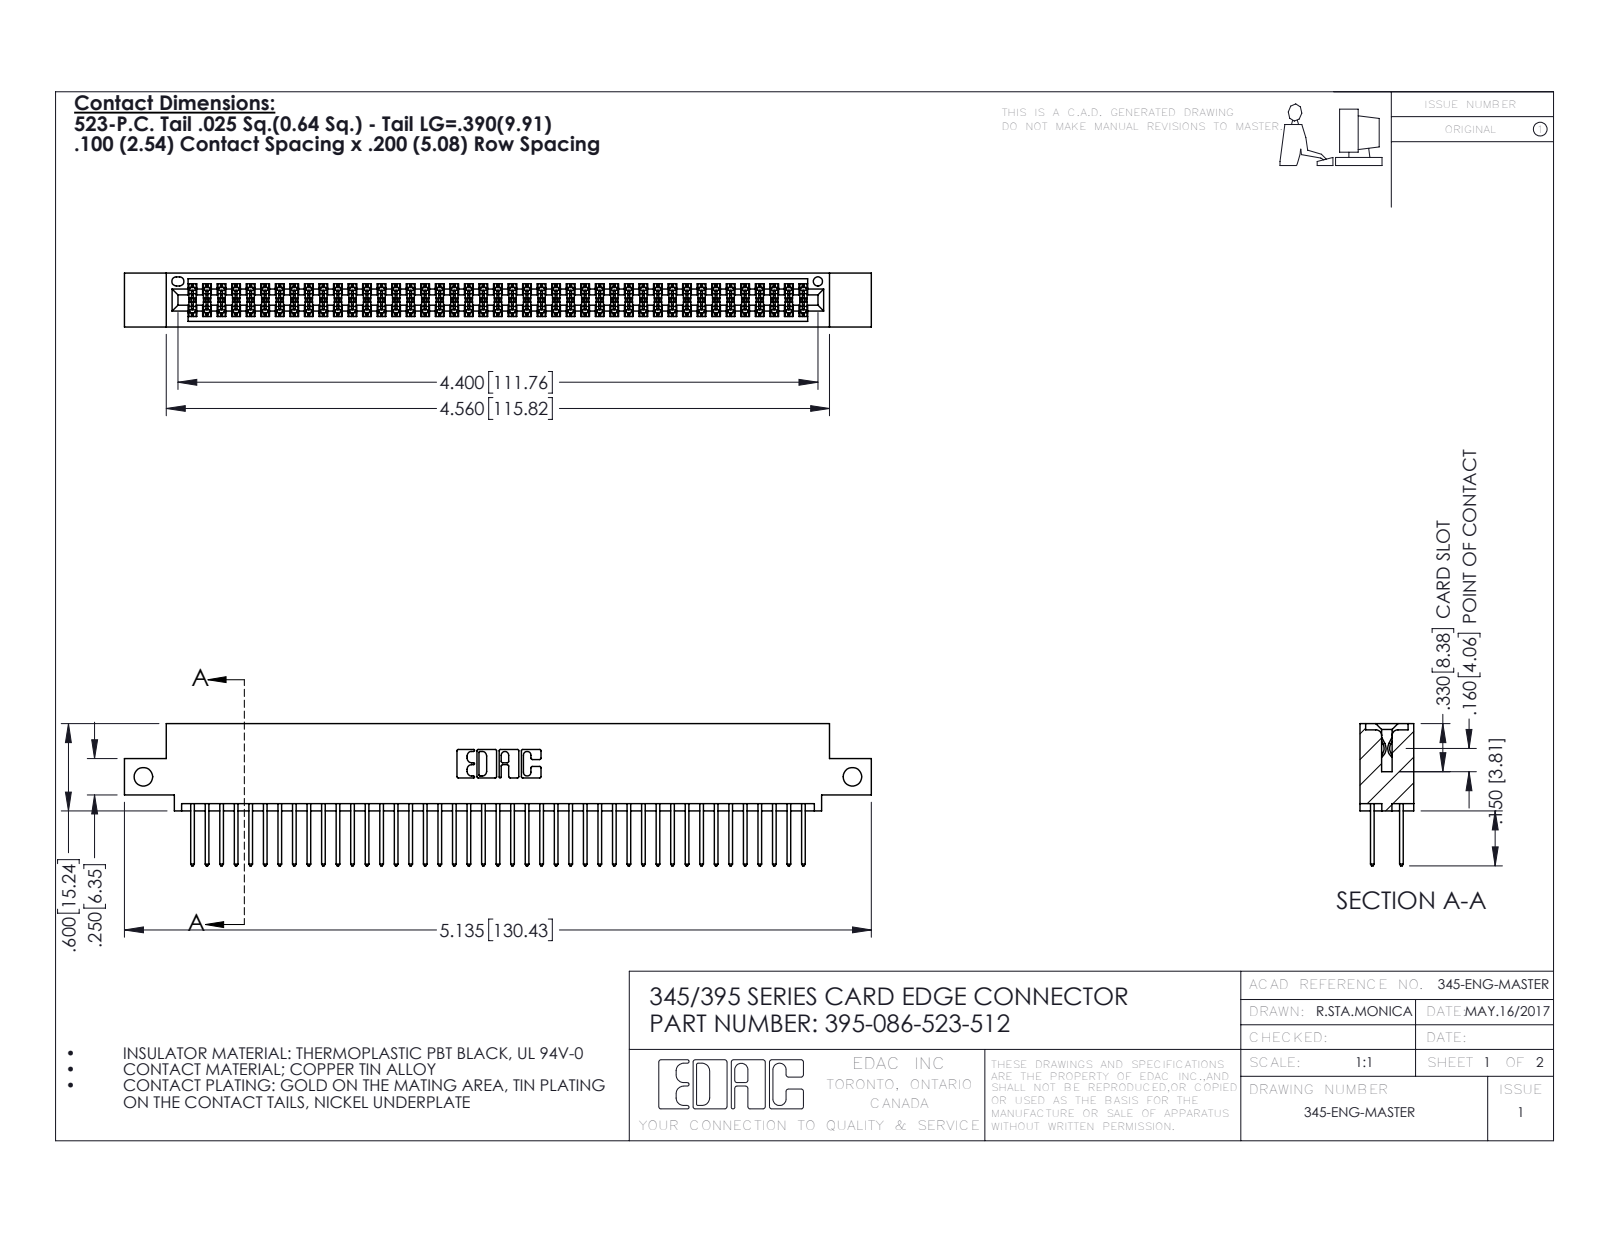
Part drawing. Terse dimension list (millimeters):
name: 395-086-523-512; 345-292-001_345-293-123; 345 Part_0.110 Offset - Side Mount
written by: SolidWorks 2016 (CONFIG_CONTROL_DESIGN)
unit: mm
bodies: 87 solids, 4430 faces (2922 planar, 1508 cylindrical, 0 other)
size: 130.4 × 24.8 × 9.4
volume: 12 700 mm³; area: 19 540 mm²
holes: 2× ⌀3.3, 1× ⌀1.6
rounds: 129× R0.2, 86× R0.3, 22× R0.3, 6× R0.2, 6× R0.8, 3× R0.7, 2× R0.4, 2× R0.5
face distances: 7.6, 1.8, 5.1, 2.5, 6.9, 0.6, 9.4, 5.7, 4.4, 3.8
hole spacings: 123.8
